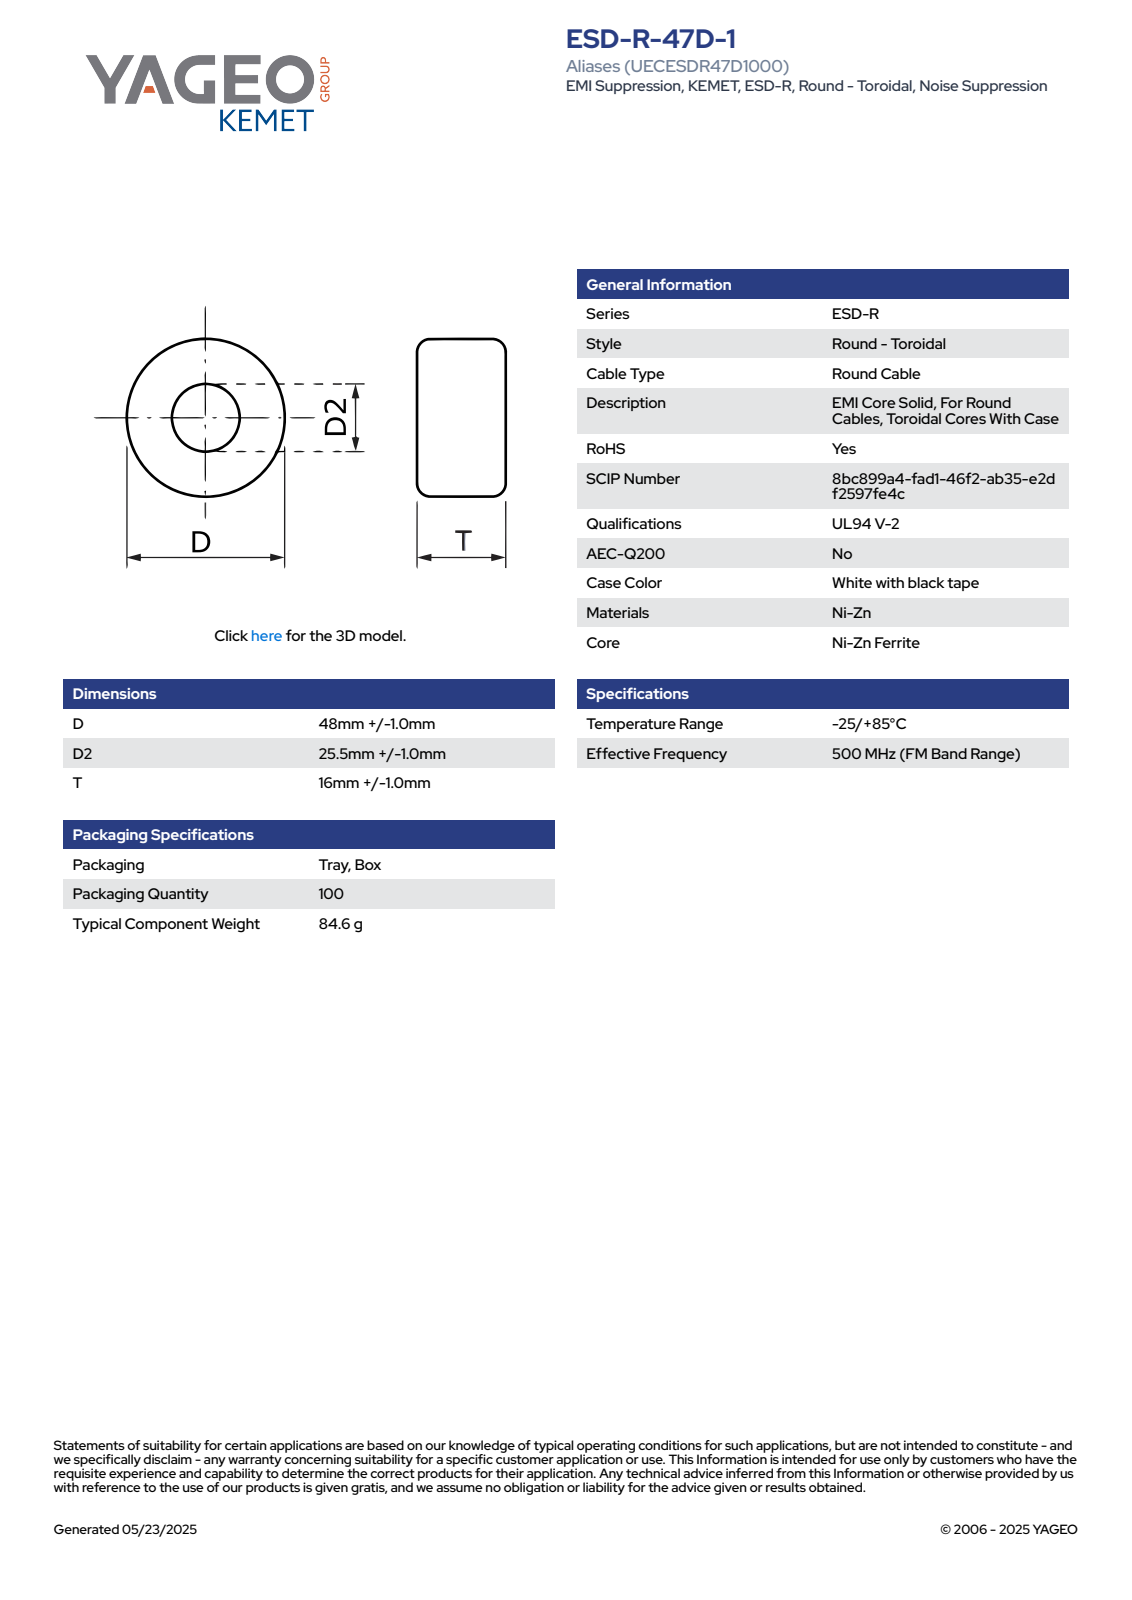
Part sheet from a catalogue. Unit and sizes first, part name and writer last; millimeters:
Units: millimetres
Overall size (bounding box): 49.01 × 49 × 17
Round holes (diameter × count): ⌀25.5 ×1
Round bosses / shafts (diameter × count): ⌀49 ×1
Partial cylindrical surfaces — rounded edges, fillets, slot ends (radius × count): R24.51 ×1
Main face-to-face distances: 17, 7.65, 9.35, 1.7, 0.32, 7.97, 9.03, 1.38, 1.06, 8.71
Volume: 23 221 mm³ · Surface area: 6 545 mm²
Bodies: 1 solid, 66 faces (24 planar, 7 cylindrical, 35 other)
Part name (STEP PRODUCT): EC_KBC_D49D225.5T17
STEP written by: SolidWorks 2021 (AUTOMOTIVE_DESIGN)
